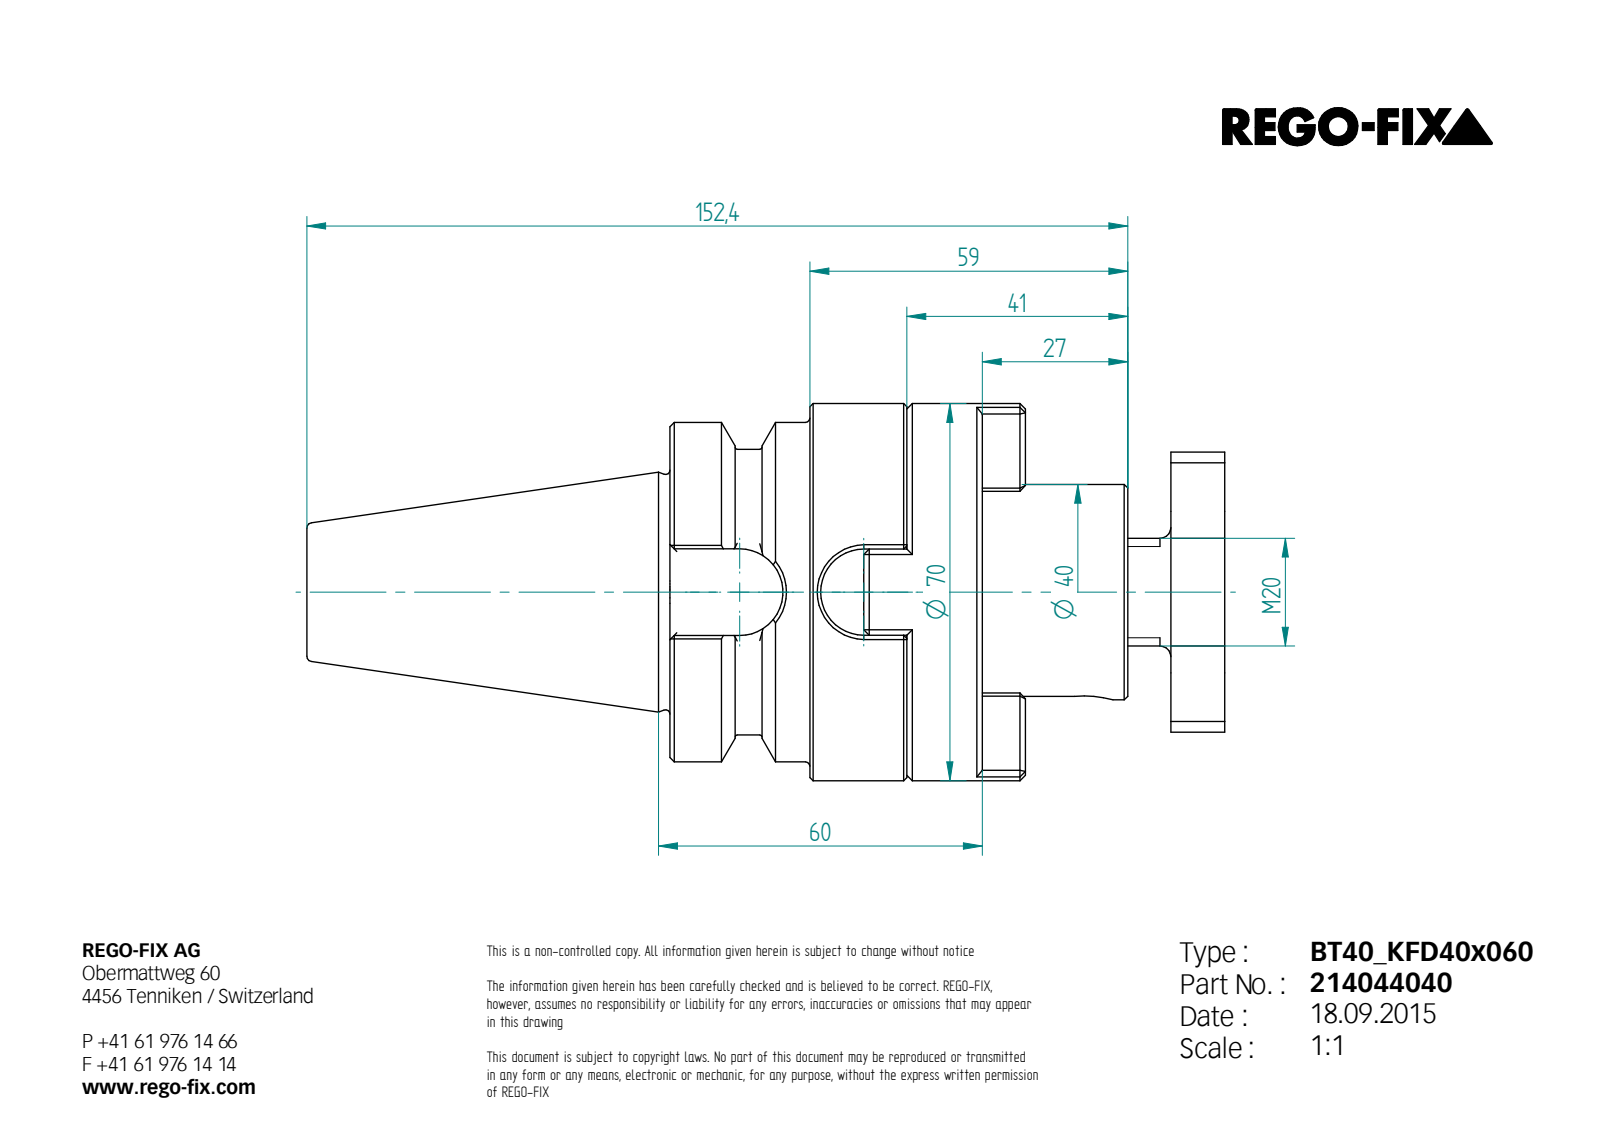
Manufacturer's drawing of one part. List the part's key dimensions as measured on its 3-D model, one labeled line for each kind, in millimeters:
STEP written by: Unknown (AUTOMOTIVE_DESIGN)
Units: millimetres
Bodies: 3 solids, 215 faces (126 planar, 35 cylindrical, 54 other)
Overall size (bounding box): 170.4 × 70 × 70
Volume: 289 968 mm³ · Surface area: 55 523 mm²
Round holes (diameter × count): ⌀13.84 ×1, ⌀17 ×1, ⌀17.29 ×1, ⌀21 ×1, ⌀40 ×1
Round bosses / shafts (diameter × count): ⌀70 ×1, ⌀63 ×1, ⌀53 ×1, ⌀39.4 ×1, ⌀20 ×1
Partial cylindrical surfaces — rounded edges, fillets, slot ends (radius × count): R5 ×6, R0.5 ×4, R8 ×1, R8.05 ×1, R26 ×1
Main face-to-face distances: 59, 14, 18, 10, 45, 49, 8, 27, 35, 44
